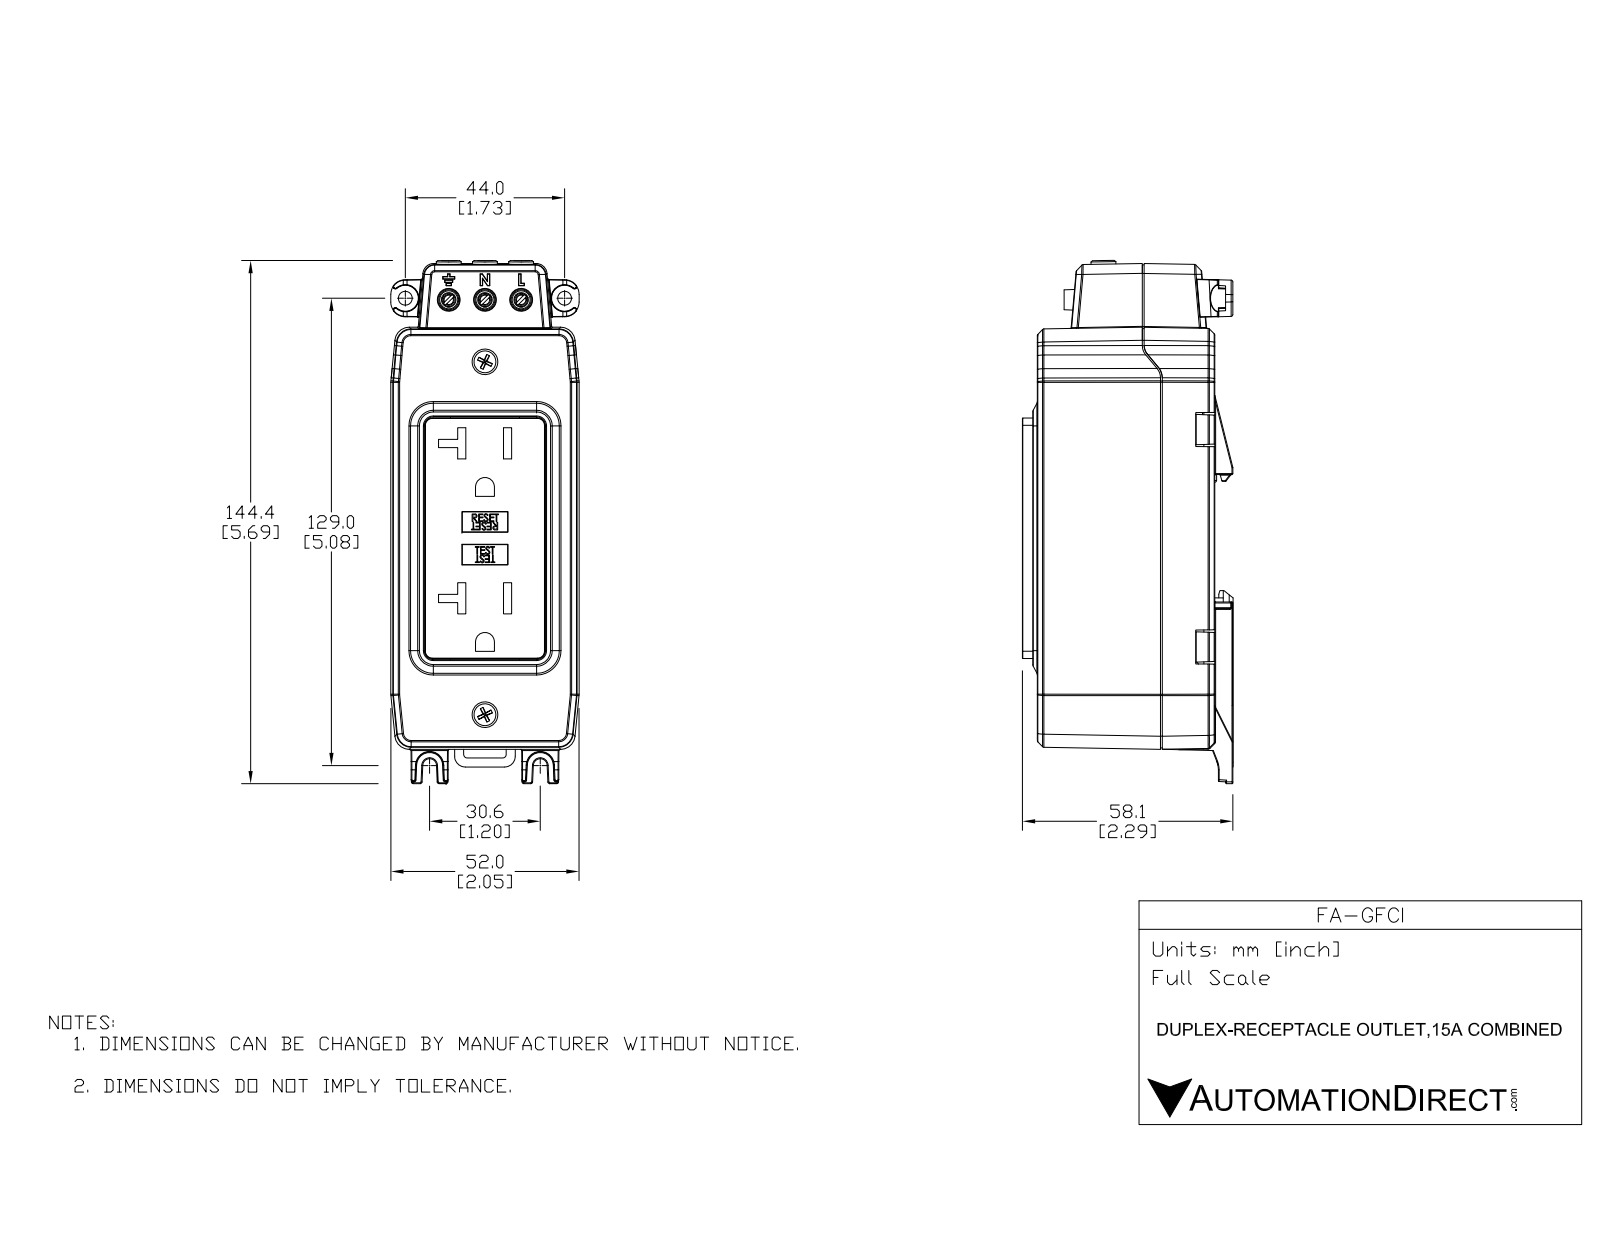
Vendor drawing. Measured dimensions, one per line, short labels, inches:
name: FA-GFCI
written by: SolidWorks 2016 (AUTOMOTIVE_DESIGN)
unit: in
bodies: 16 solids, 3102 faces (1533 planar, 868 cylindrical, 701 other)
size: 5.687 × 2.289 × 2.047
volume: 12.45 in³; area: 156.6 in²
holes: 8× ⌀0.112, 5× ⌀0.157, 4× ⌀0.102, 4× ⌀0.171, 3× ⌀0.044, 3× ⌀0.118, 3× ⌀0.248, 2× ⌀0.107, 2× ⌀0.138, 2× ⌀0.144, 2× ⌀0.279
bosses: 3× ⌀0.102, 3× ⌀0.039, 2× ⌀0.138, 1× ⌀0.315, 1× ⌀0.142, 1× ⌀0.138, 1× ⌀0.1
rounds: 165× R0.02, 164× R0.01, 52× R0.039, 38× R0.008, 32× R0.004, 18× R0.157, 16× R0.049, 12× R0.025
face distances: 0.118, 1.811, 0.119, 1.929, 1.693, 2.047, 2.091, 1.972, 0.28, 0.161
hole spacings: 0.394, 0.278, 0.295, 0.431, 0.433, 0.951, 1.113, 1.141
